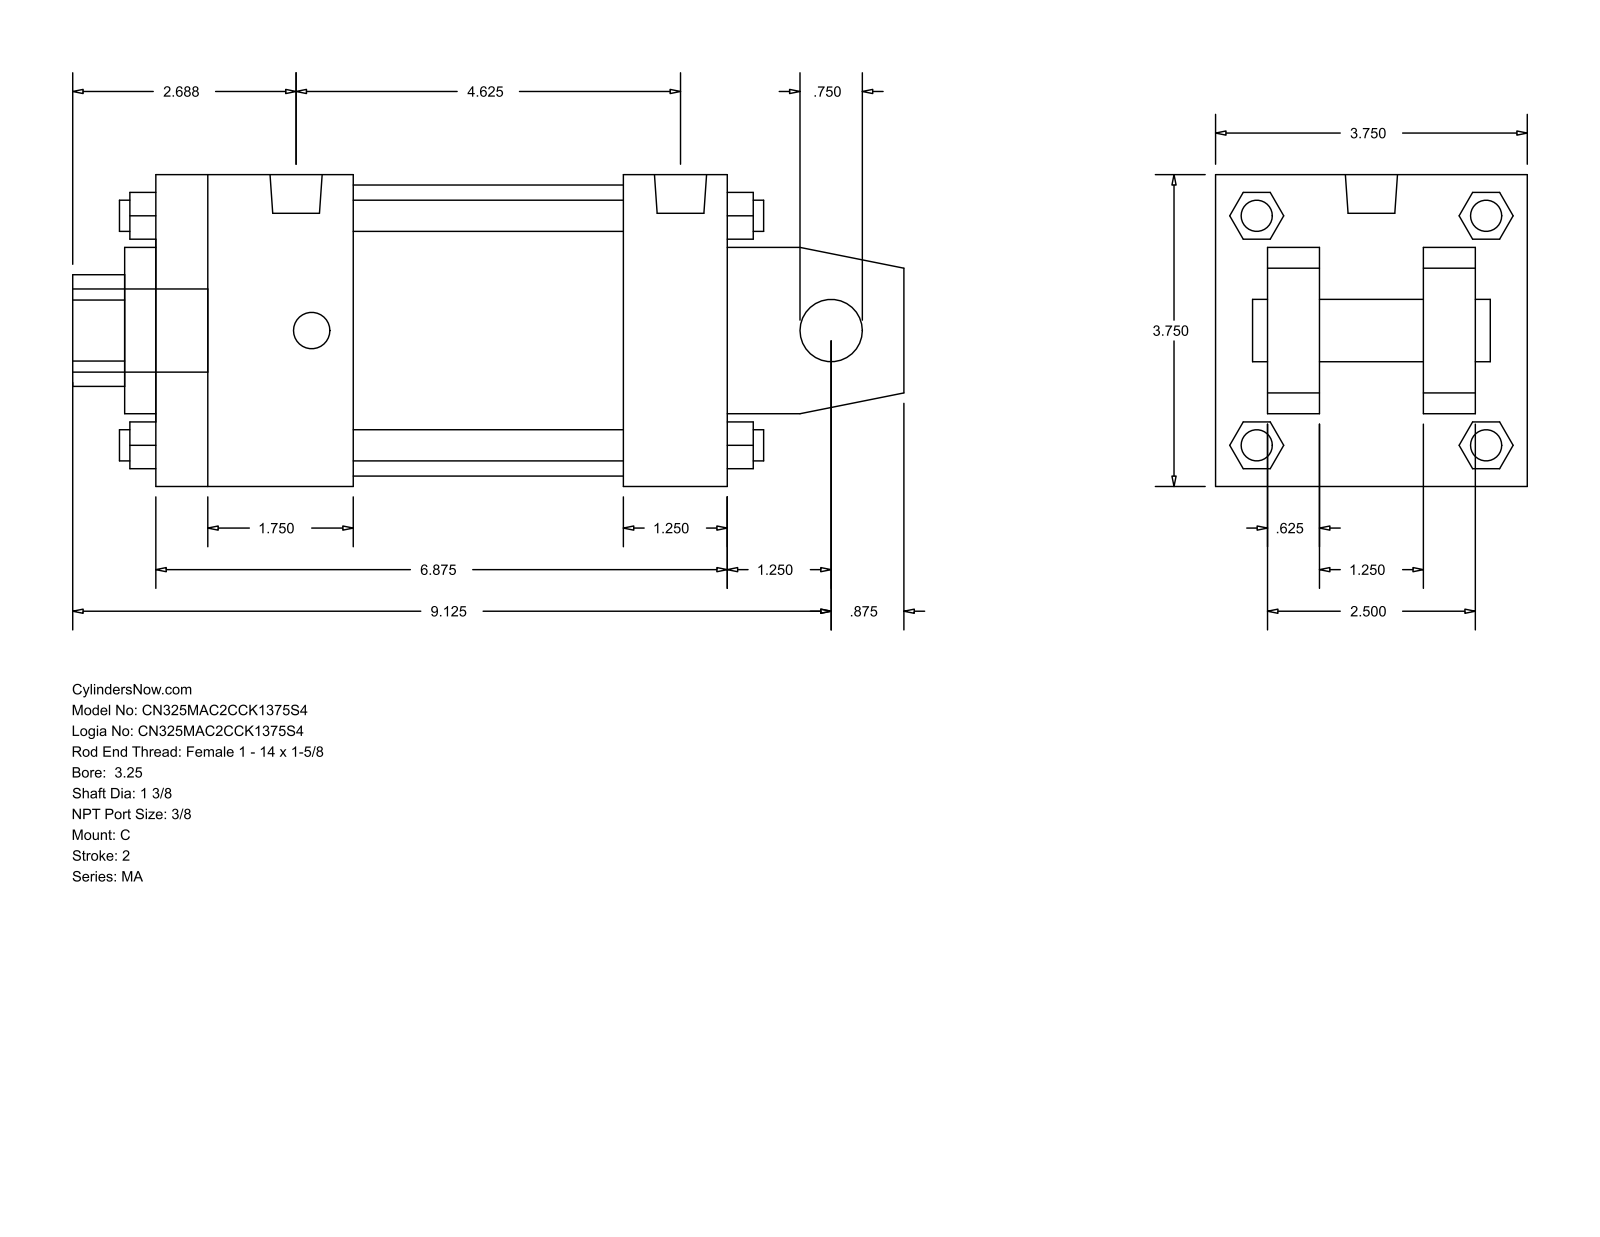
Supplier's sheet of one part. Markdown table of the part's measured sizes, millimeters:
| quantity | value |
| --- | --- |
| part name | MA_C__0325_1.375 |
| STEP written by | GSSL Pune (CONFIG_CONTROL_DESIGN) |
| units | millimeters |
| bodies | 0 solids, 139 faces (108 planar, 31 cylindrical, 0 other) |
| overall size | 254 × 95.25 × 95.25 |
| round holes (diameter × count) | 19.05 × 1, 34.92 × 1, 50.8 × 1, 88.9 × 1 |
| round bosses / shafts (diameter × count) | 11.11 × 4, 9.53 × 4, 15.93 × 2, 25.4 × 1 |
| partial cylindrical surfaces (radius × count) | 17.06 × 1 |
| main face-to-face distances | 95.24, 15.87, 63.5, 174.63, 31.74, 79.37, 47.63, 142.88, 31.75, 60.32 |
